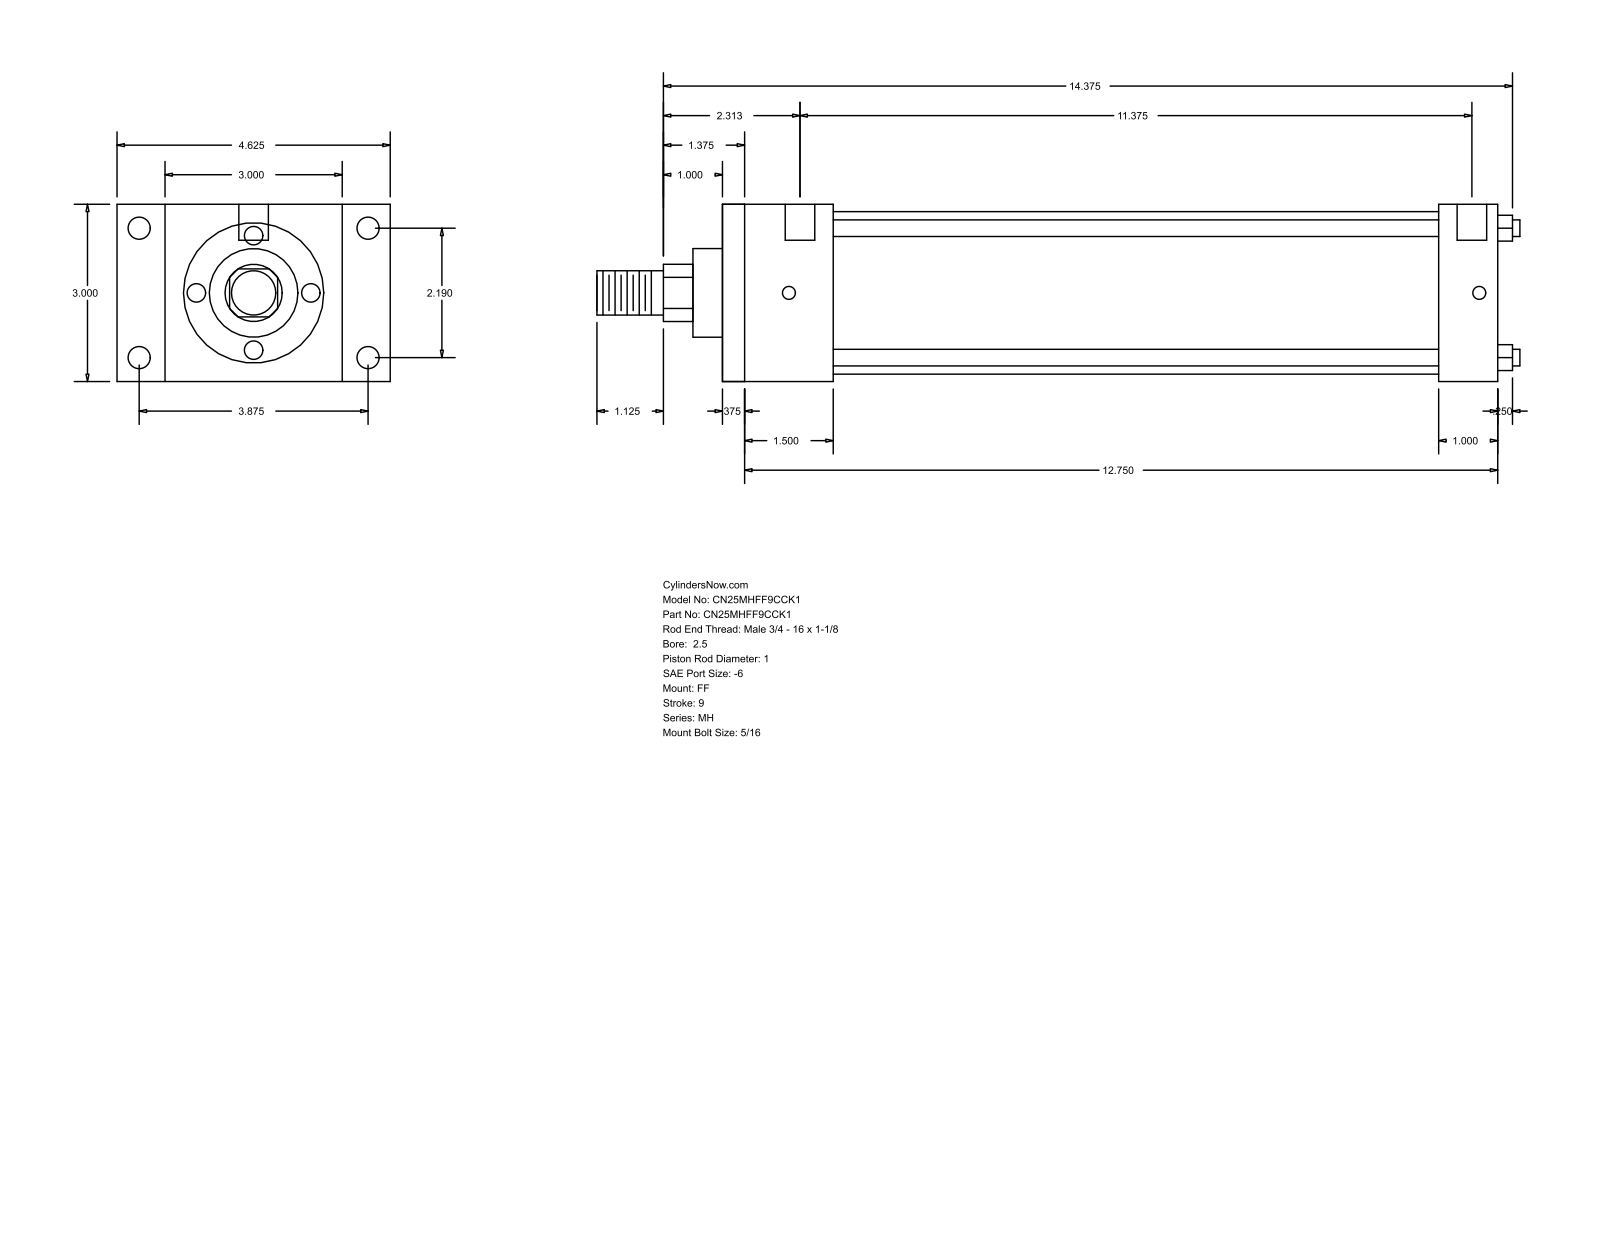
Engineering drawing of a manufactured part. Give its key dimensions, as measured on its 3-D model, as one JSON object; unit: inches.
{"part_name": "MH_FF__0250_1", "step_written_by": "GSSL Pune (CONFIG_CONTROL_DESIGN)", "units": "inches", "bodies": {"solids": 0, "faces": 92, "planar": 64, "cylindrical": 28, "other": 0}, "overall_size": [15.625, 4.625, 3], "round_holes": [[0.219, 4], [0.375, 4], [0.5, 2]], "round_bosses_or_shafts": [[0.281, 4], [2.75, 1], [1.5, 1], [1, 1], [0.75, 1]], "partial_cylinders_radius": [[0.484, 1]], "face_to_face_distances": [3, 13.125, 12.75, 0.375, 1, 1.875, 12.125, 1.5, 11.75, 10.25], "hole_center_spacings": [2.19, 3.875, 4.451, 11.687, 0.125, 0.187, 11.375, 11.5]}
